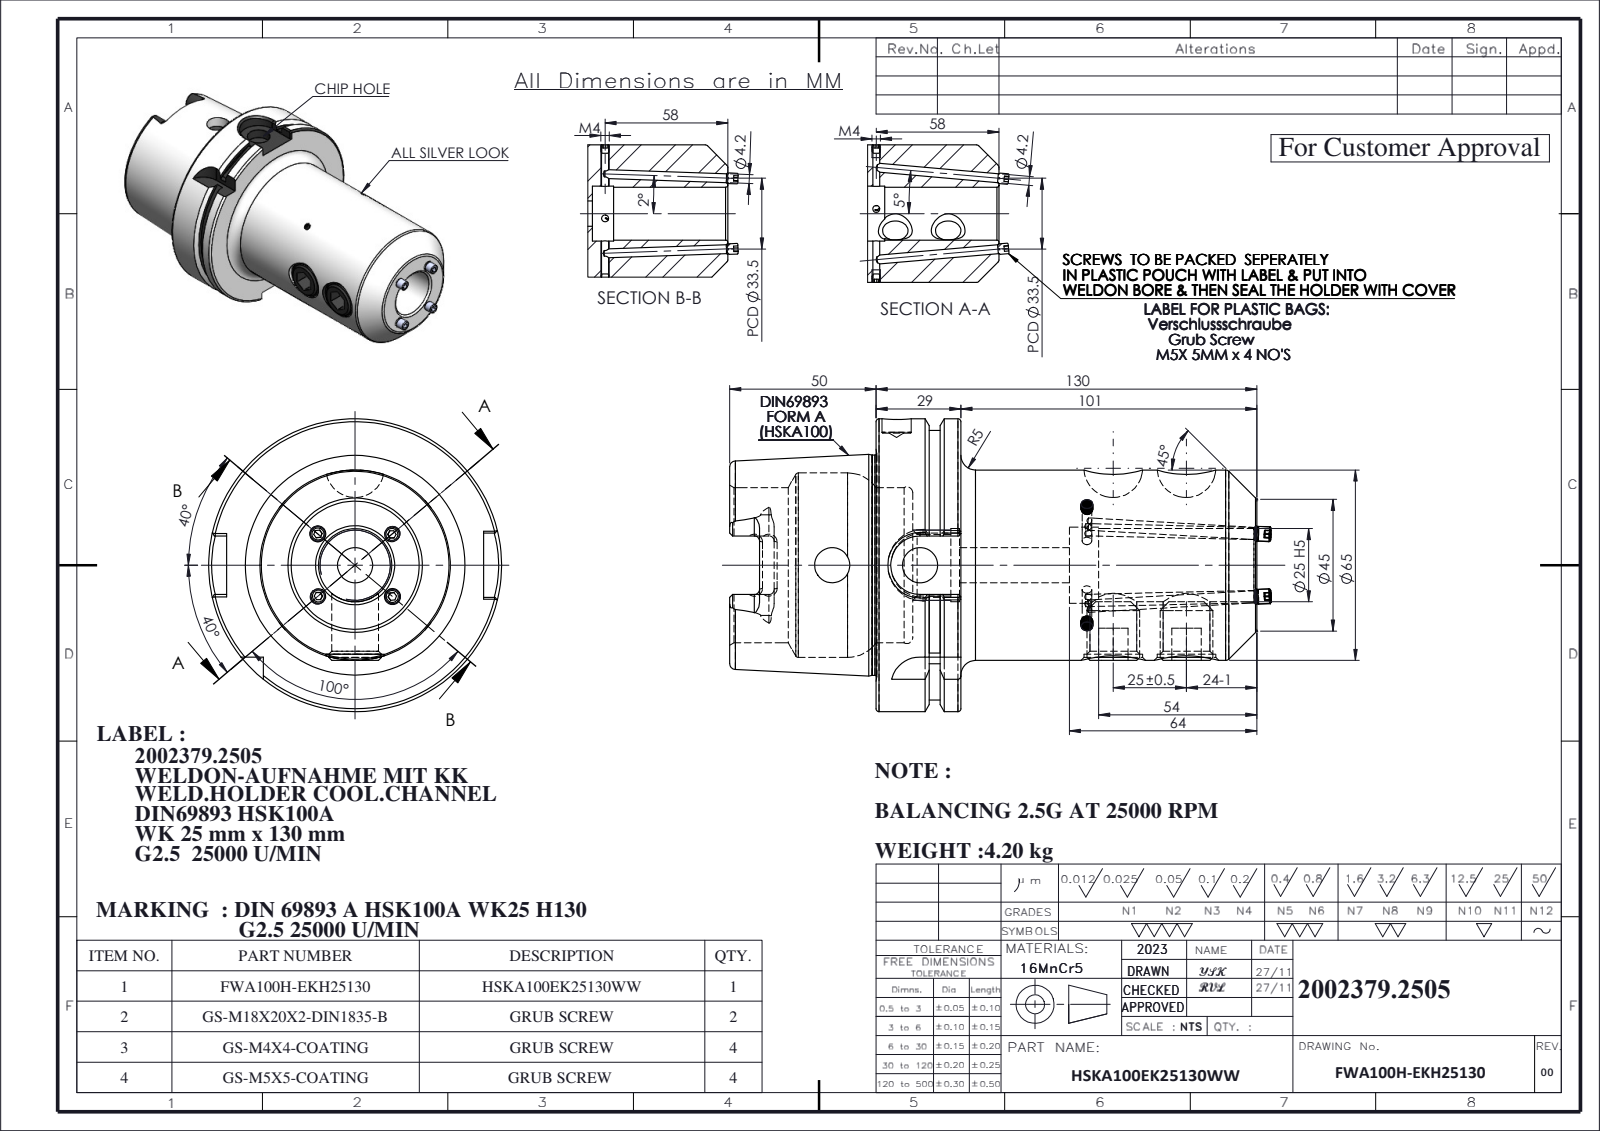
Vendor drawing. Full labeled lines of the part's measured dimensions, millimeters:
Part name (STEP PRODUCT): HSKA100EK25130WW; GS-M4X4_DIN 913 - M4 x 4-N; GS-M5X5_DIN 913 - M5 x 5-N; GS-M18X20X2-DIN1835-B (+1 more)
STEP written by: SolidWorks 2023 (CONFIG_CONTROL_DESIGN)
Units: millimetres
Bodies: 11 solids, 515 faces (145 planar, 132 cylindrical, 238 other)
Overall size (bounding box): 184.89 × 100 × 100
Volume: 537 079 mm³ · Surface area: 84 951 mm²
Round holes (diameter × count): ⌀3.3 ×4, ⌀4.2 ×4, ⌀12 ×3, ⌀16 ×2, ⌀20 ×2, ⌀10 ×1, ⌀21 ×1, ⌀25 ×1, ⌀26 ×1, ⌀53 ×1, ⌀63 ×1
Round bosses / shafts (diameter × count): ⌀5 ×4, ⌀4 ×4, ⌀18 ×2, ⌀100 ×1, ⌀92 ×1, ⌀75.16 ×1, ⌀65 ×1
Partial cylindrical surfaces — rounded edges, fillets, slot ends (radius × count): R1.8 ×6, R4.88 ×4, R10 ×2, R11 ×1
Main face-to-face distances: 28.95, 12.5, 16.45, 50, 62.5, 78.95, 180, 130, 117.5, 101.05
Hole centre spacings: 25, 30, 74, 99
